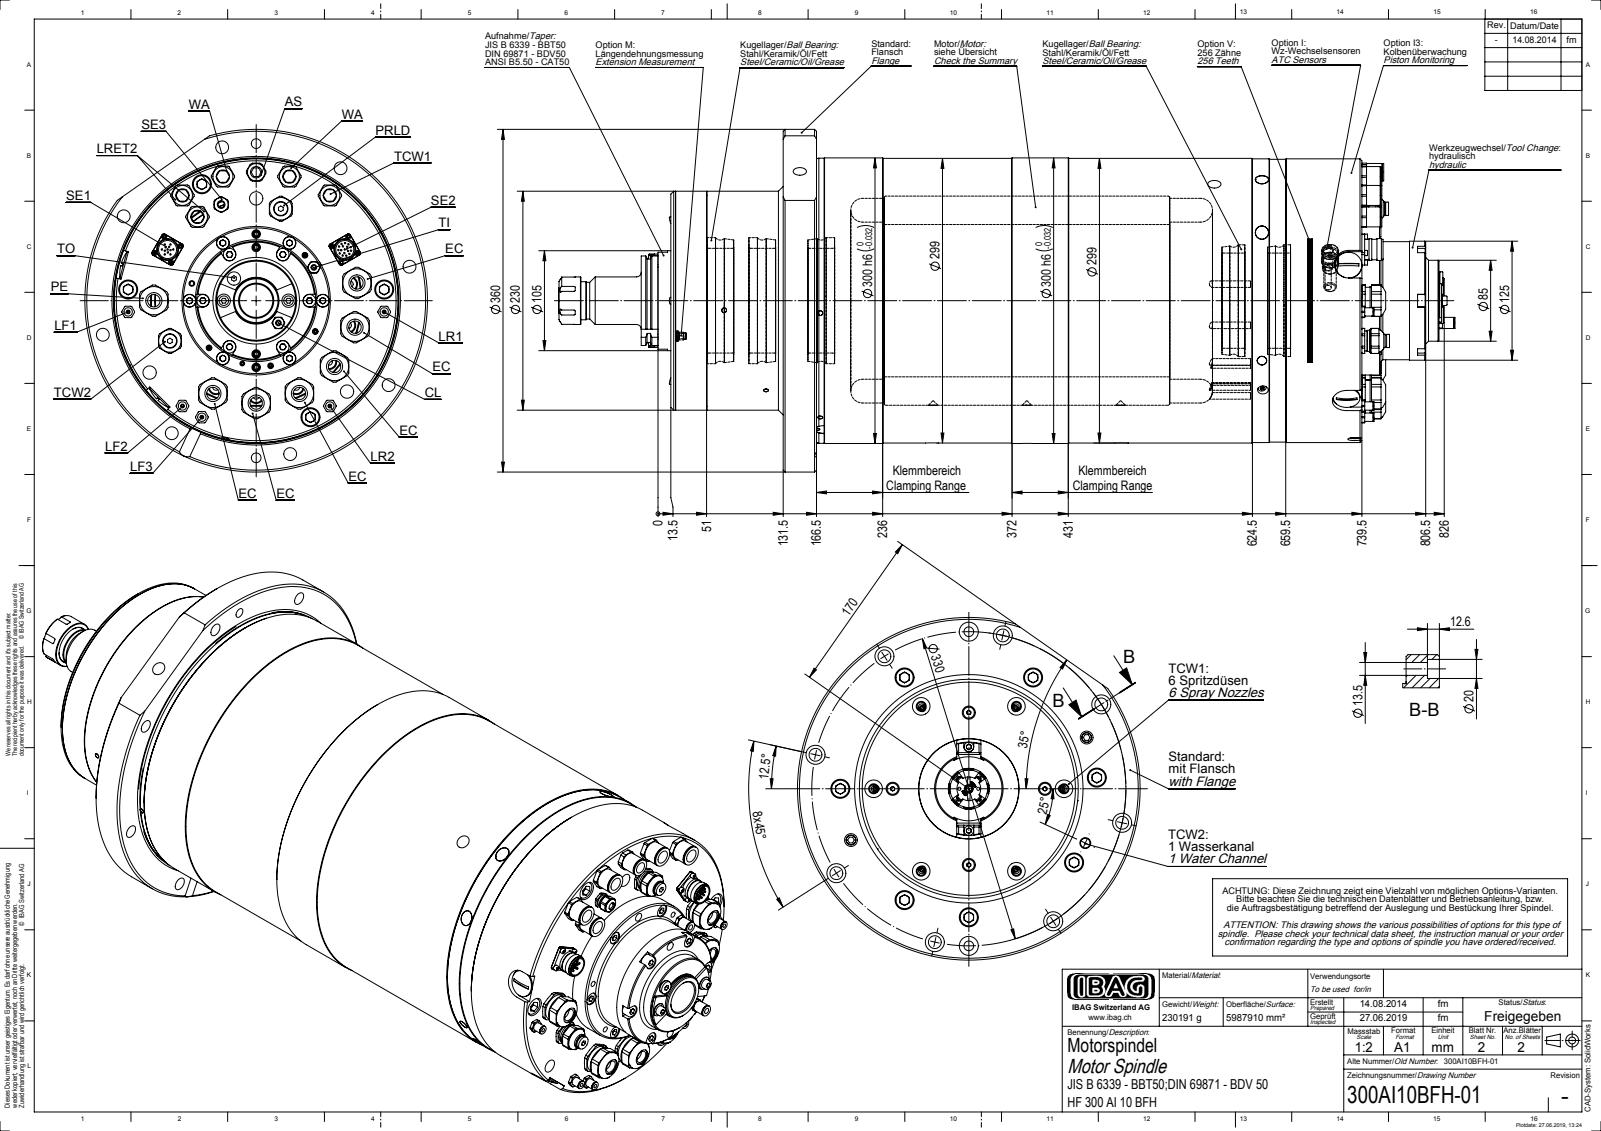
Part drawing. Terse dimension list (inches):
name: 300AI10BFH-01
written by: SolidWorks 2014 (CONFIG_CONTROL_DESIGN)
unit: in
bodies: 0 solids, 1810 faces (712 planar, 792 cylindrical, 306 other)
size: 37.073 × 14.173 × 14.173
holes: 20× ⌀0.787, 16× ⌀0.531, 13× ⌀0.551, 7× ⌀0.197, 7× ⌀0.236, 7× ⌀0.492, 7× ⌀0.669, 6× ⌀0.413, 5× ⌀0.157, 5× ⌀0.472, 4× ⌀0.354, 3× ⌀1.181
bosses: 28× ⌀0.059, 8× ⌀0.217, 7× ⌀1.173, 7× ⌀1.111, 7× ⌀1.04, 7× ⌀0.512, 6× ⌀0.276, 5× ⌀0.827
rounds: 12× R0.039, 7× R0.26, 7× R0.65, 6× R0.266, 5× R0.325, 5× R0.482, 2× R0.52, 2× R0.591
face distances: 23.937, 4.528, 19.409, 4.449, 23.858, 28.386, 0.197, 4.646, 24.055, 28.583
hole spacings: 5.315, 3.937, 6.496, 12.003, 6.819, 1.741, 4.777, 7.45
